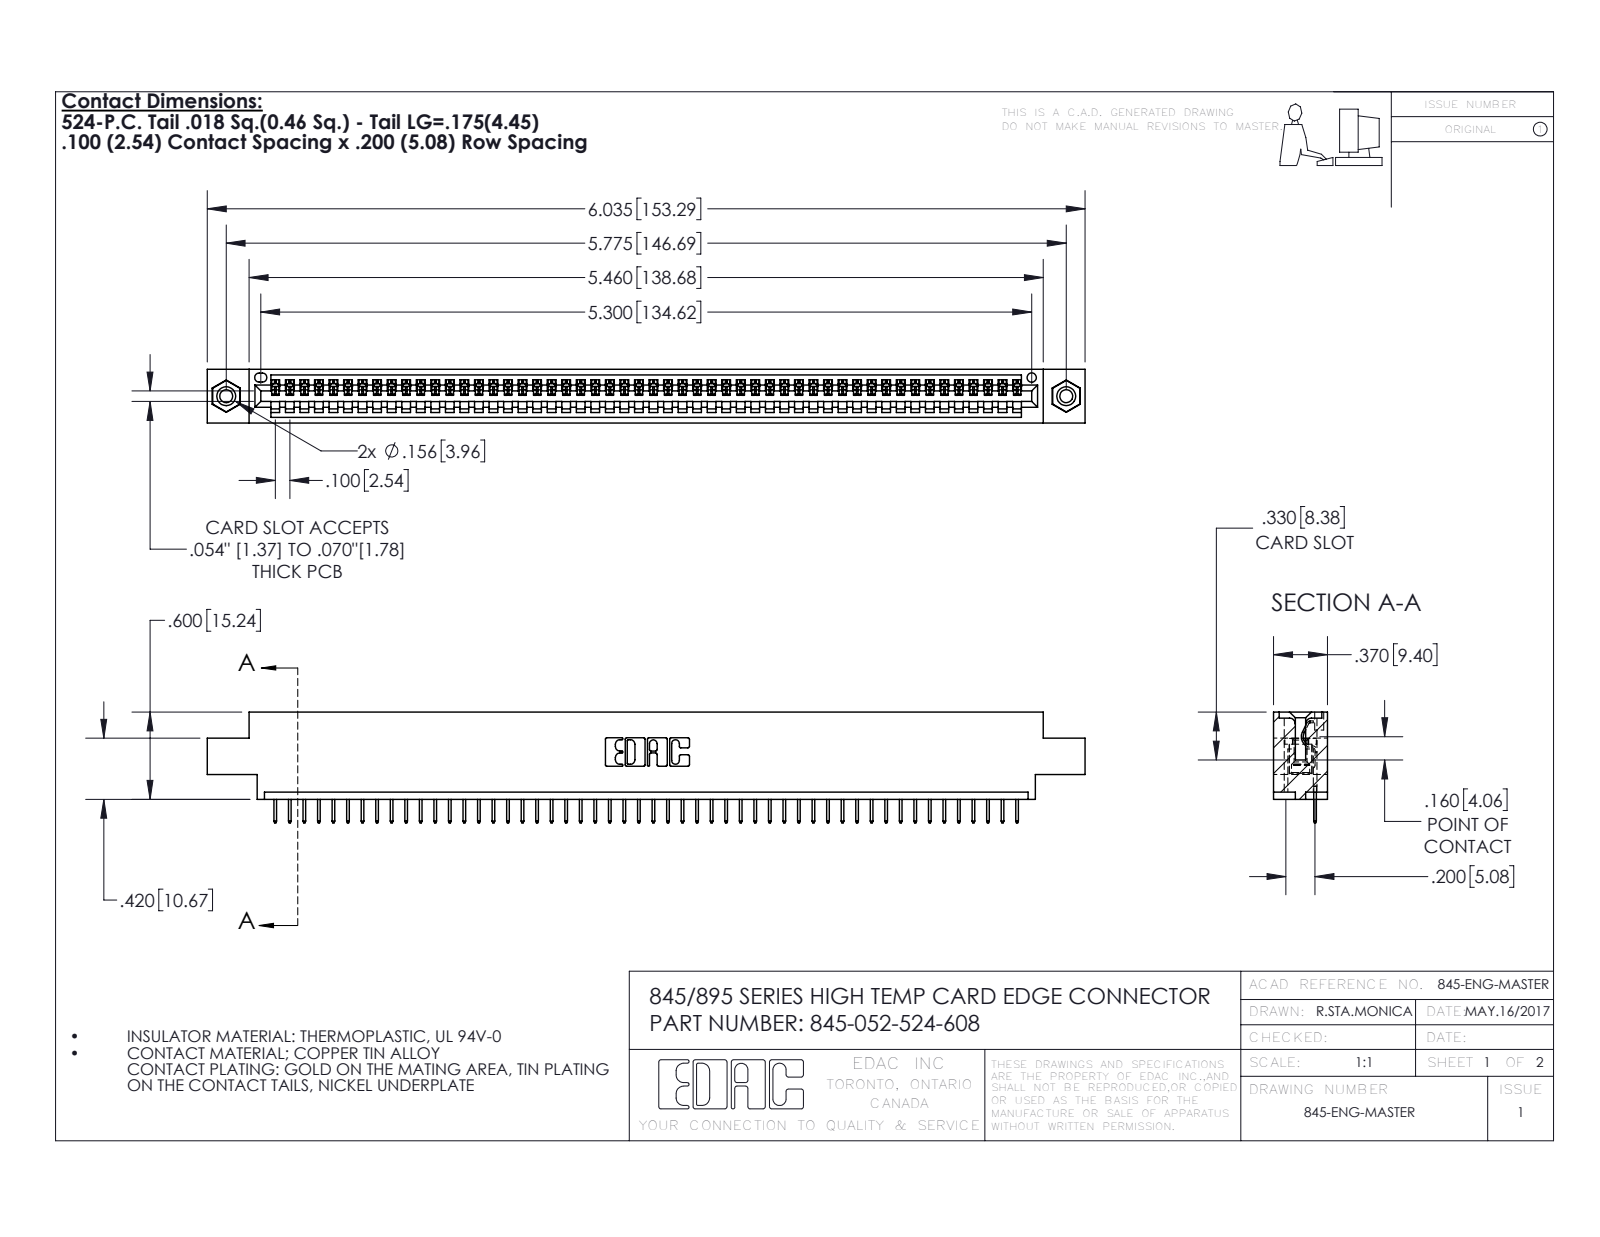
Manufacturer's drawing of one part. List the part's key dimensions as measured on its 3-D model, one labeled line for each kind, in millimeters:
Part name (STEP PRODUCT): 345 Part_0.170 Offset - 0.156 Dia-TI; 345-052-524-608; 345-250-001_345-250-003-102; 345-292-001_345-293-124
STEP written by: SolidWorks 2016 (CONFIG_CONTROL_DESIGN)
Units: millimetres
Bodies: 55 solids, 3414 faces (2508 planar, 890 cylindrical, 16 other)
Overall size (bounding box): 153.3 × 19.4 × 9.4
Volume: 14 300 mm³ · Surface area: 18 650 mm²
Round holes (diameter × count): ⌀2.3 ×2, ⌀3.2 ×2, ⌀4 ×2, ⌀1.6 ×1
Round bosses / shafts (diameter × count): ⌀3.9 ×2
Partial cylindrical surfaces — rounded edges, fillets, slot ends (radius × count): R0.2 ×104, R0.3 ×22, R0.2 ×6, R0.8 ×6, R0.7 ×3, R0.8 ×2, R1 ×2, R0.4 ×1
Main face-to-face distances: 1.8, 7.6, 9.4, 5.1, 2.5, 6.9, 0.6, 5.7, 1.8, 4.4
Hole centre spacings: 6.9, 140.7, 146.7
